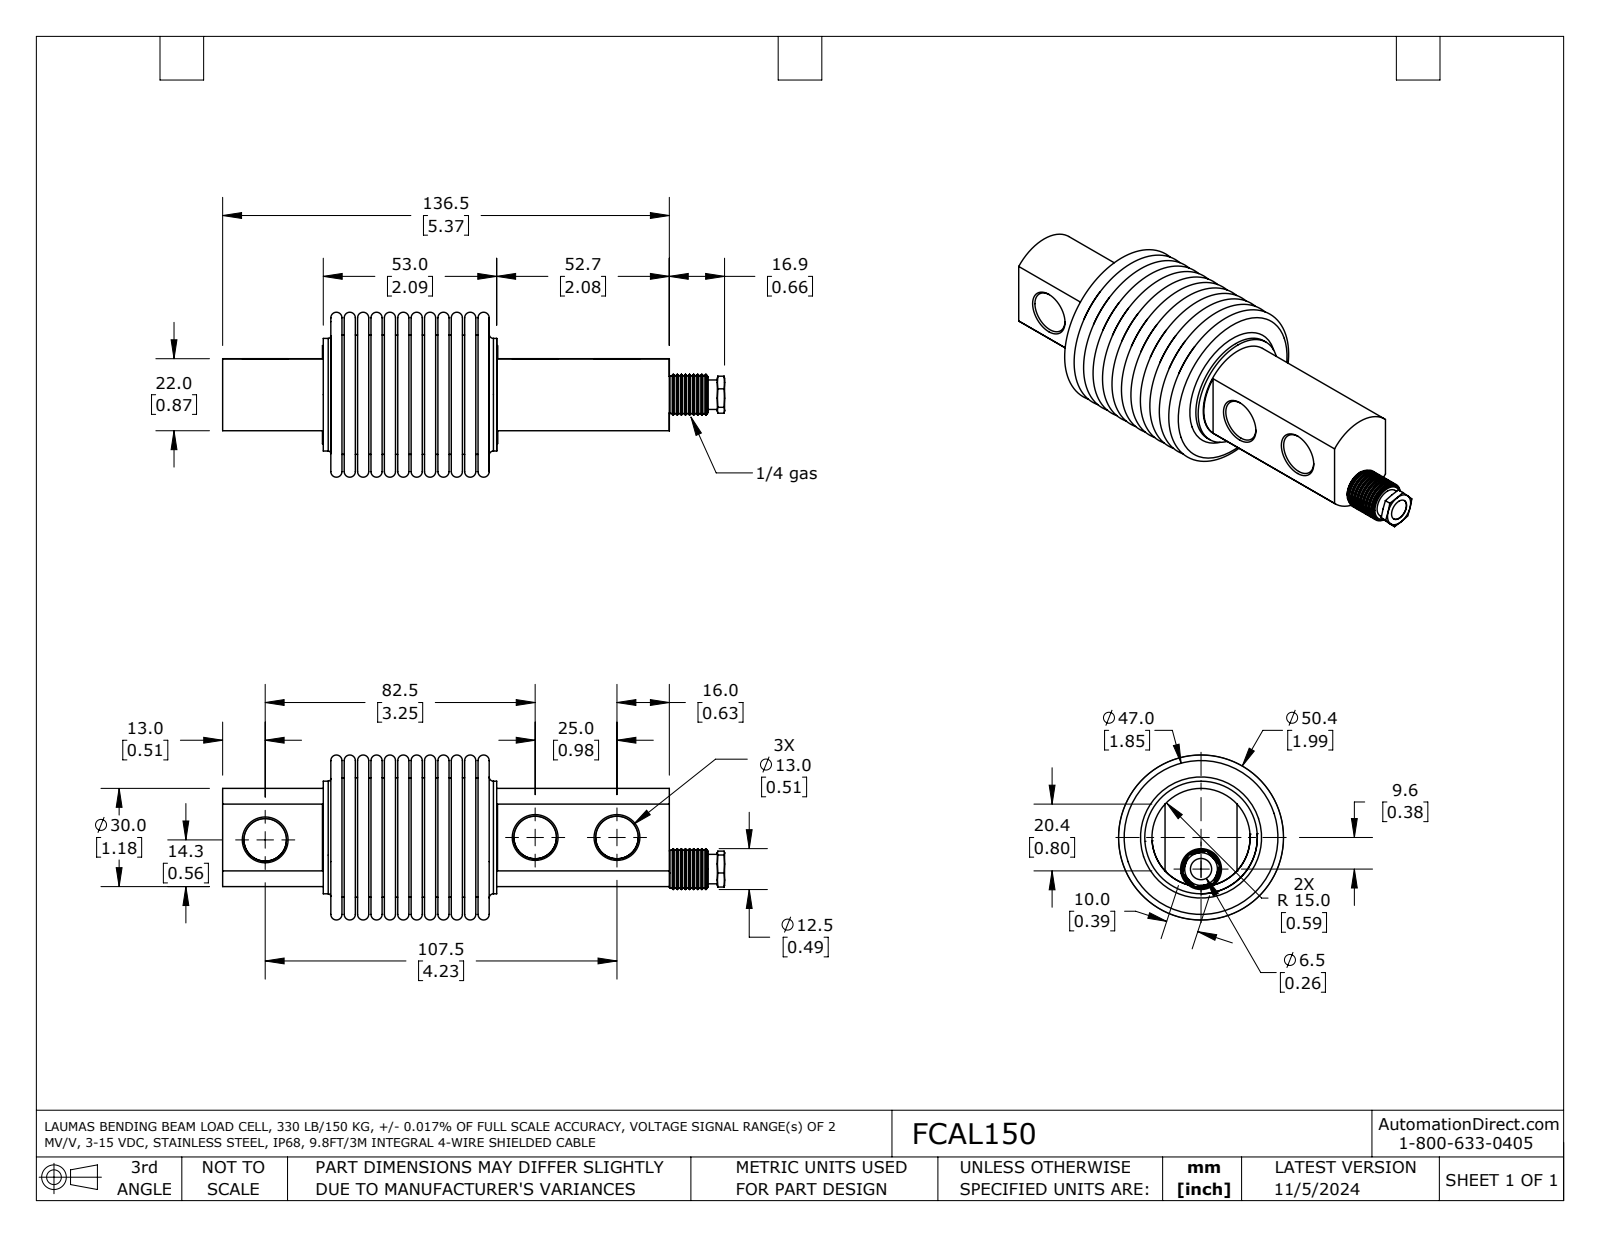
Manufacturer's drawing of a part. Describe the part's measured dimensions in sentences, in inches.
The part is named "FCAL150". Its 3-D file was written by "SolidWorks 2021 (AUTOMOTIVE_DESIGN)". It is 2 solids with 378 faces: 32 planar, 30 cylindrical and 316 other. Overall it measures 6.039 by 1.984 by 1.984 inches. Its volume is 5.302 cubic inches and its surface area 117.2 square inches. Round holes: 3 of diameter 0.512, 1 of diameter 0.256, 1 of diameter 0.394. Round bosses or shafts: 1 of diameter 1.354, 1 of diameter 1.339, 1 of diameter 1.181, 1 of diameter 0.453, 1 of diameter 0.354. The main face-to-face distances are 1.897, 0.866, 1.889, 1.905, 4.072, 4.065, 2.175, 2.167, 1.302, 1.309. The hole center spacings are 0.984, 3.248, 4.232.
